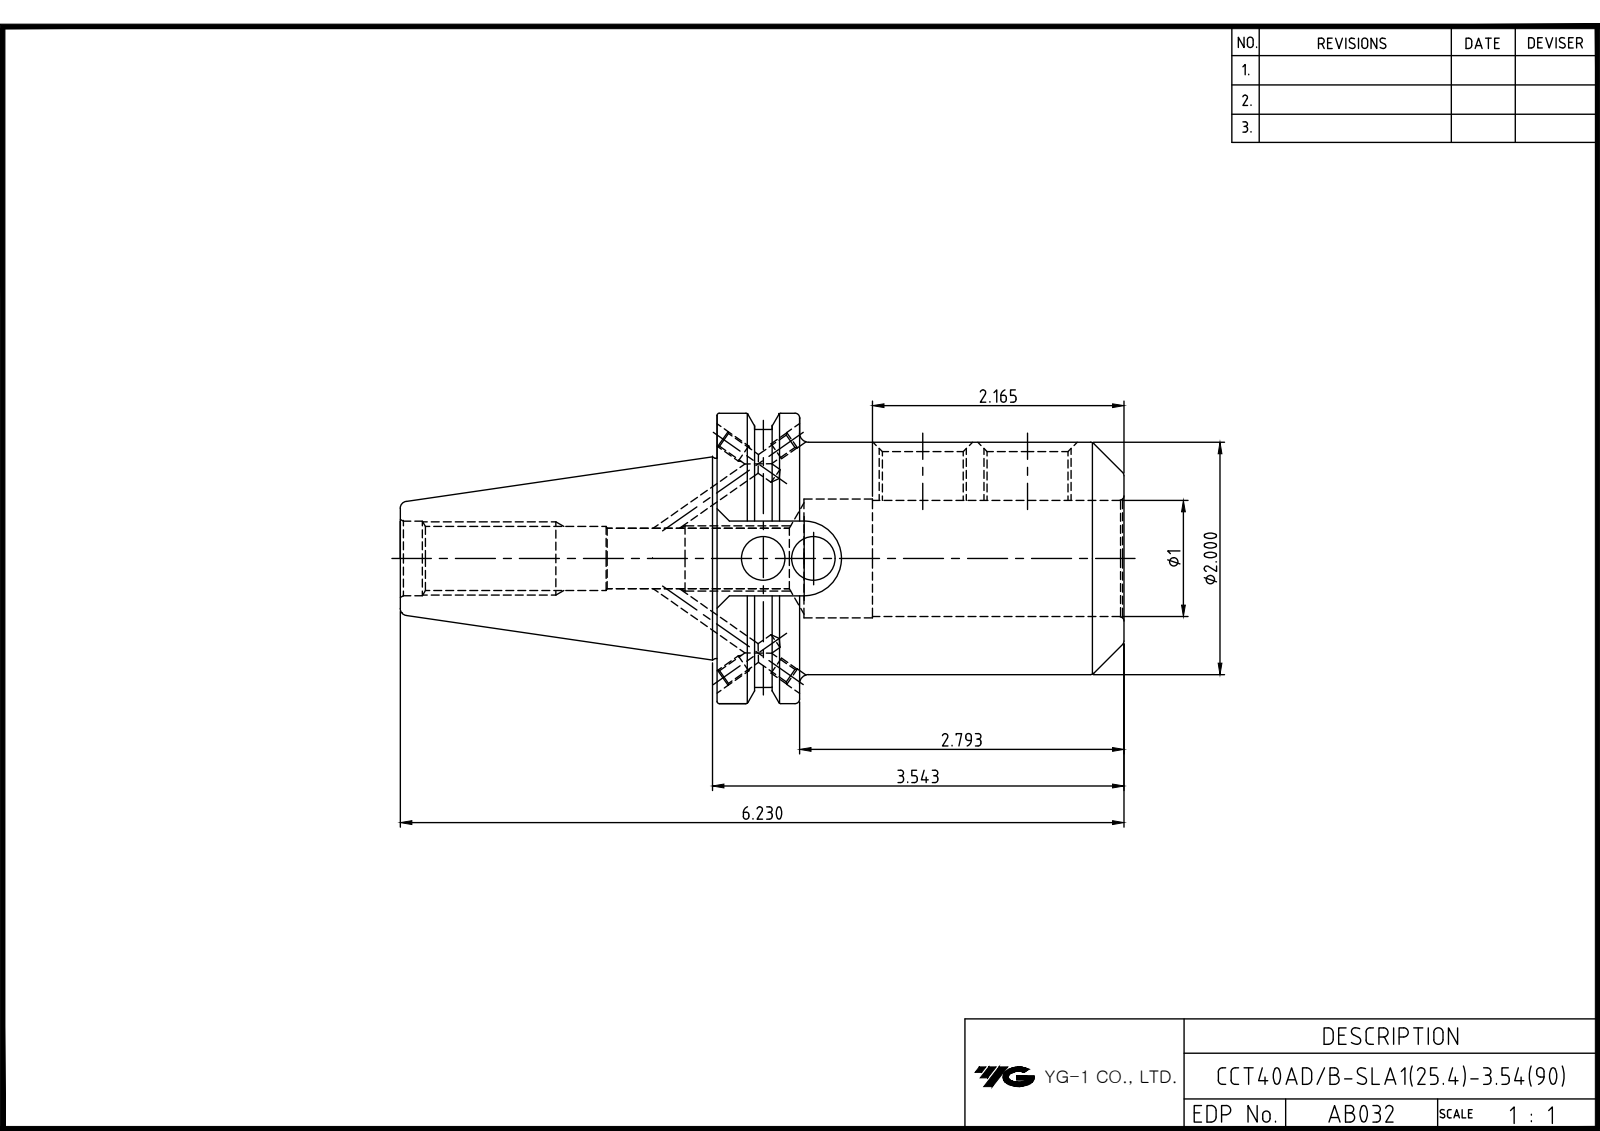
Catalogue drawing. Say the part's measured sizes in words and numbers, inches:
The part is named "LO-CCT40ADB-SLA25.4-90". Its 3-D file was written by "Autodesk Inventor 2025 (AUTOMOTIVE_DESIGN)". It is 1 solid with 89 faces: 33 planar, 30 cylindrical and 26 other. Overall it measures 6.23 by 2.5 by 2.405 inches. Its volume is 12.29 cubic inches and its surface area 58.77 square inches. Round holes: 4 of diameter 0.128, 4 of diameter 0.157, 2 of diameter 0.682, 1 of diameter 0.375, 1 of diameter 0.495, 1 of diameter 0.527, 1 of diameter 0.642, 1 of diameter 1, 1 of diameter 1.047. Round bosses or shafts: 1 of diameter 2.5, 1 of diameter 2.217, 1 of diameter 2, 1 of diameter 1.724. Partial cylindrical surfaces (rounded edges, fillets, slot ends): 1 of radius 0.322. The main face-to-face distances are 0.711, 3.504, 2.793, 0.748, 0.037, 2.756, 1.874, 0.645, 2.726, 3.437. The hole center spacings are 1.334, 0.902.
